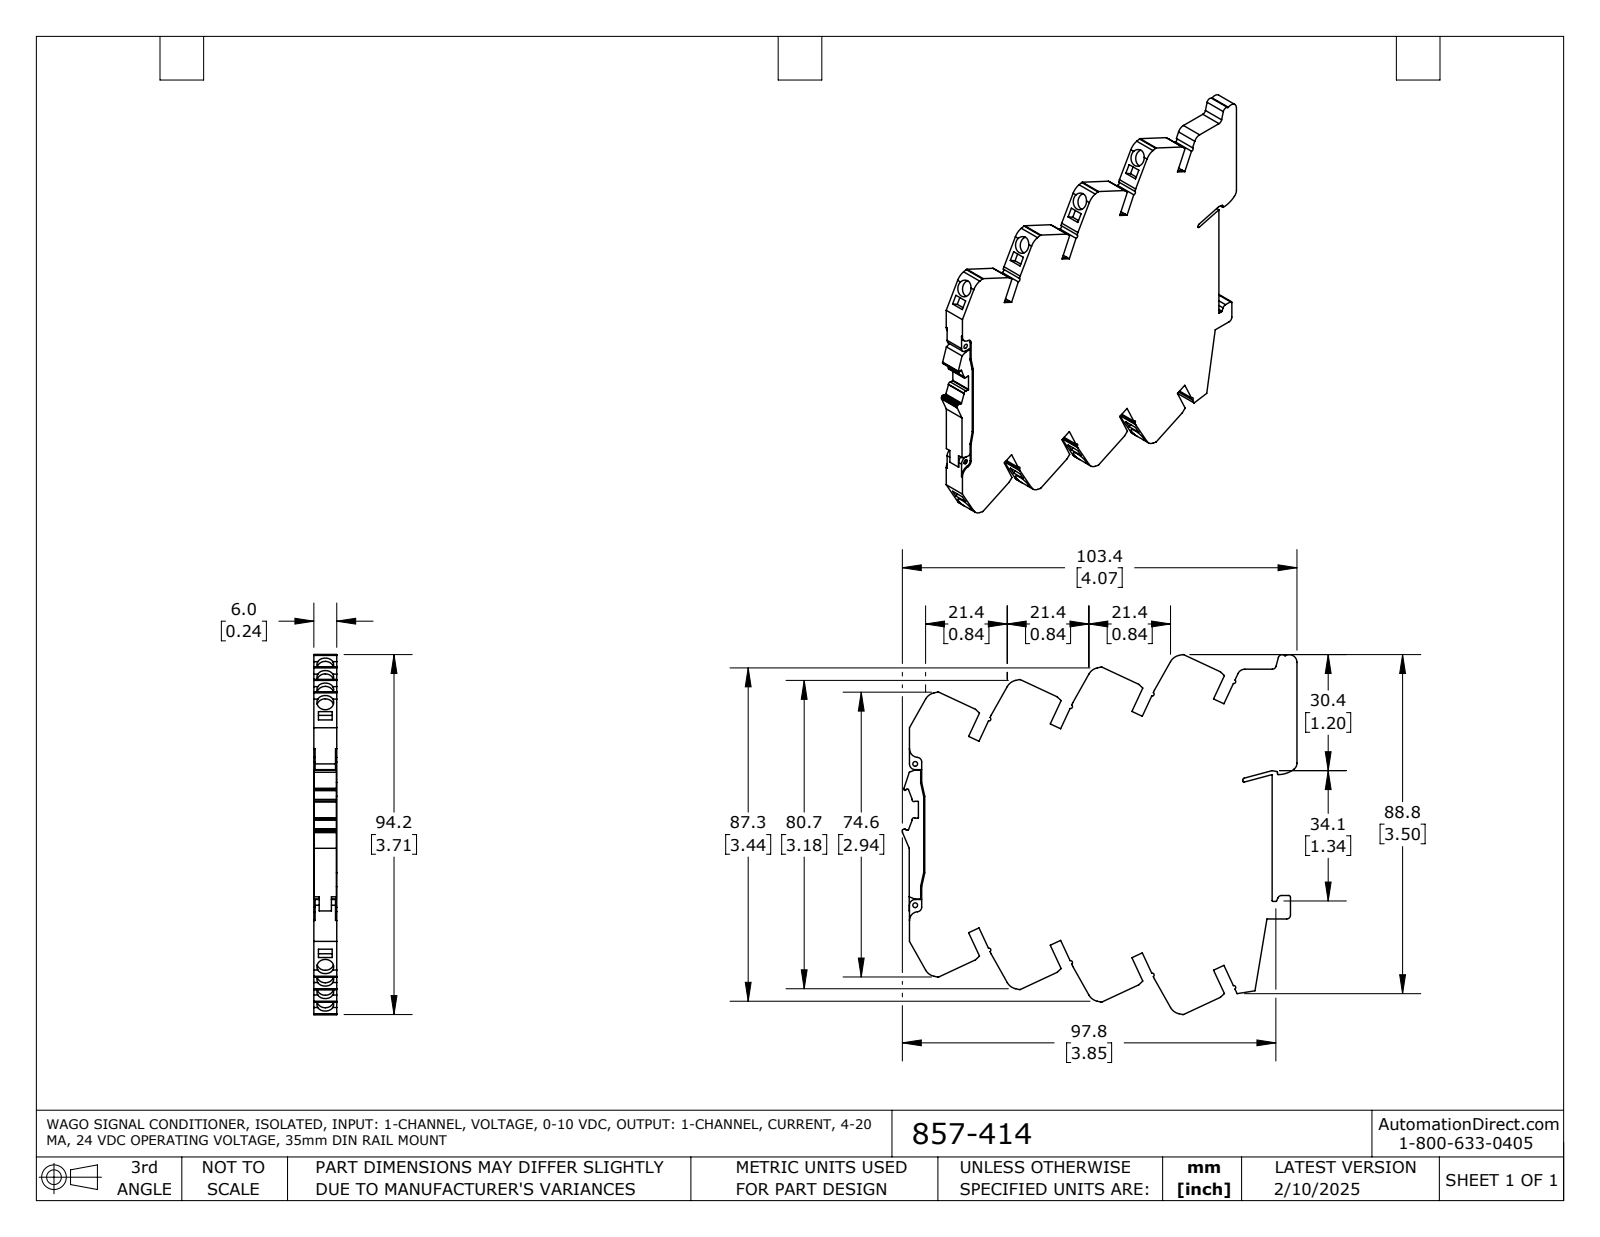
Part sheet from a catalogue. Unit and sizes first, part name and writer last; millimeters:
Units: millimetres
Overall size (bounding box): 103.4 × 94.3 × 6
Round holes (diameter × count): ⌀4.4 ×8, ⌀1.2 ×2
Partial cylindrical surfaces — rounded edges, fillets, slot ends (radius × count): R0.5 ×12, R0.2 ×11, R0.4 ×8, R3.4 ×8, R1 ×4, R0.3 ×3, R2 ×3, R0.5 ×2
Main face-to-face distances: 6, 18, 17, 12, 5.9, 12, 3, 24, 36, 6.5
Hole centre spacings: 13.4, 13.3, 26.7, 26.7, 26.7, 37, 40, 40.1
Volume: 43 930 mm³ · Surface area: 19 260 mm²
Bodies: 1 solid, 317 faces (219 planar, 98 cylindrical, 0 other)
Part name (STEP PRODUCT): 857-414
STEP written by: SolidWorks 2021 (AUTOMOTIVE_DESIGN)
